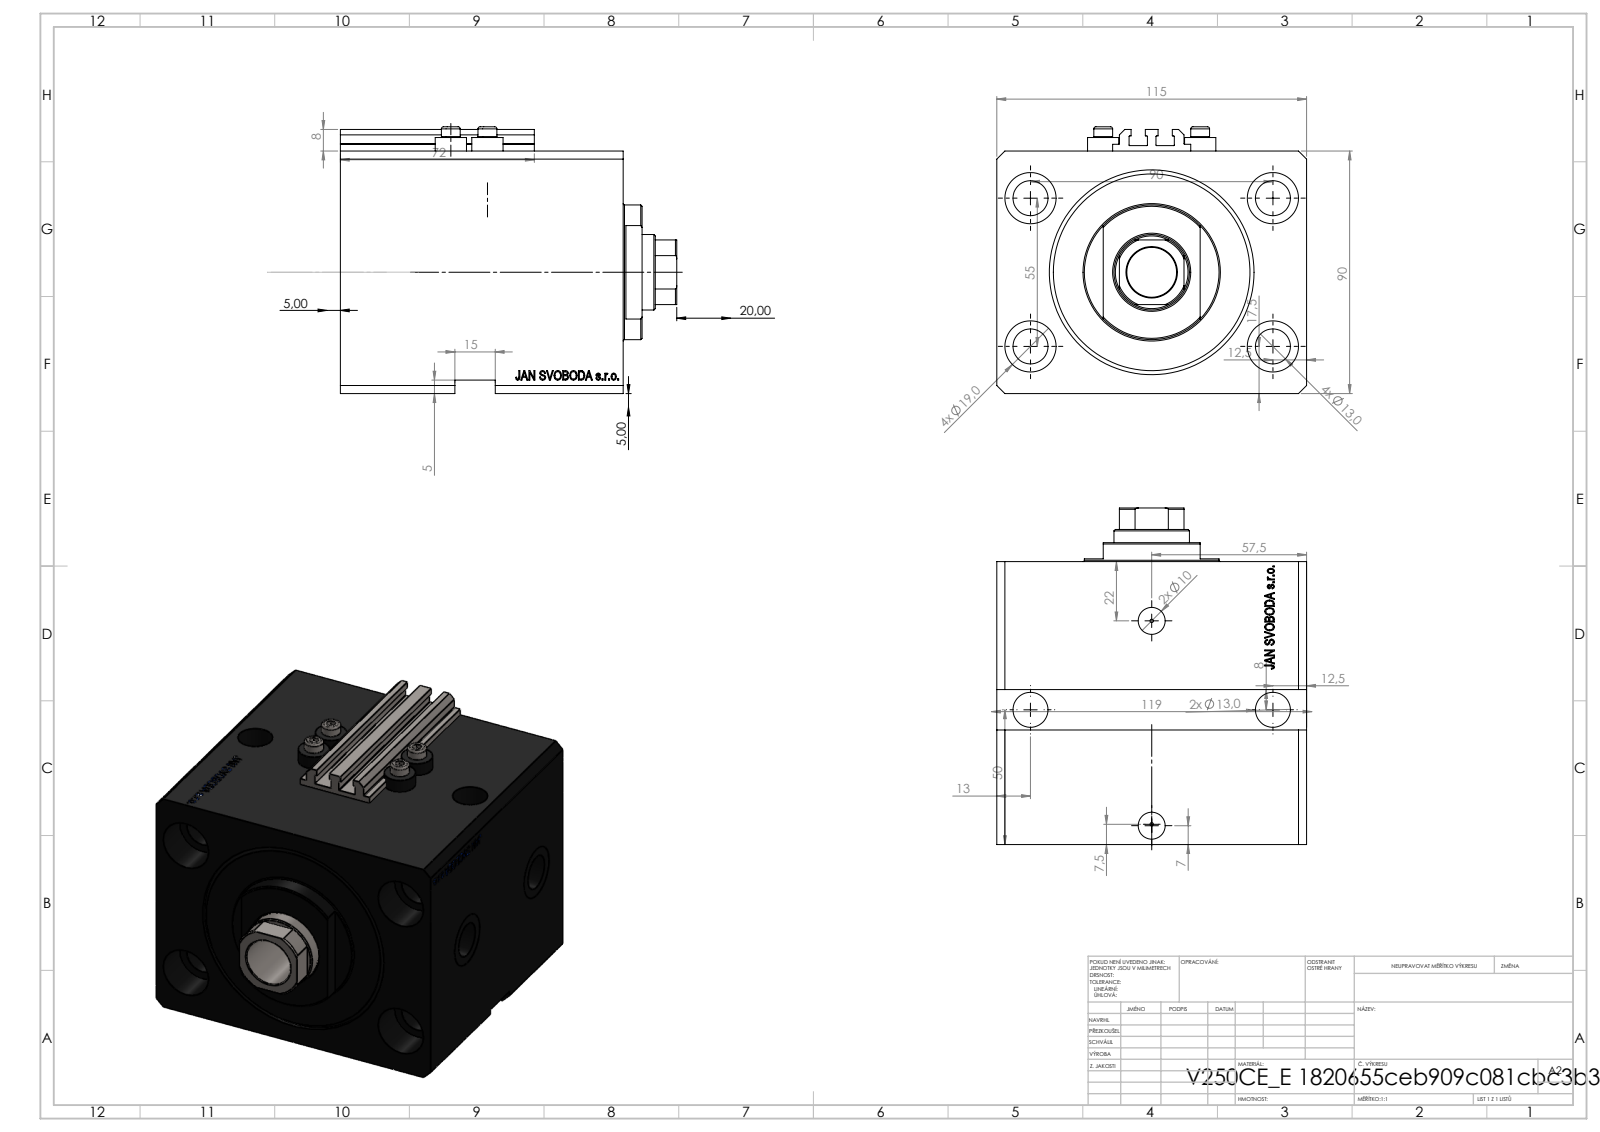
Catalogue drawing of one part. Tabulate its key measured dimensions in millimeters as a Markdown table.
| quantity | value |
| --- | --- |
| part name | V250CE_E_Body; ALLEN BOLT V250CE; V250CE_VC_E; V250CE_C_VCP |
| STEP written by | SolidWorks 2019 (CONFIG_CONTROL_DESIGN) |
| units | millimeters |
| bodies | 8 solids, 1107 faces (543 planar, 126 cylindrical, 438 other) |
| overall size | 124.9 × 115 × 99 |
| volume | 954 523 mm³ |
| surface area | 156 491 mm² |
| round holes (diameter × count) | 13 × 6, 1.25 × 4, 4 × 4, 19 × 4, 10 × 2, 13.16 × 2, 20 × 2, 18.5 × 1, 28 × 1, 63 × 1, 76 × 1 |
| round bosses / shafts (diameter × count) | 11.6 × 4, 7 × 4, 50 × 1 |
| partial cylindrical surfaces (radius × count) | 0.2 × 10, 13.5 × 1 |
| main face-to-face distances | 90, 115, 105, 87.1, 17.9, 57, 74.9, 30.1, 20, 54.9 |
| hole center spacings | 52.74, 55, 90, 13.6, 27.39, 28.46, 33.62, 36 |
